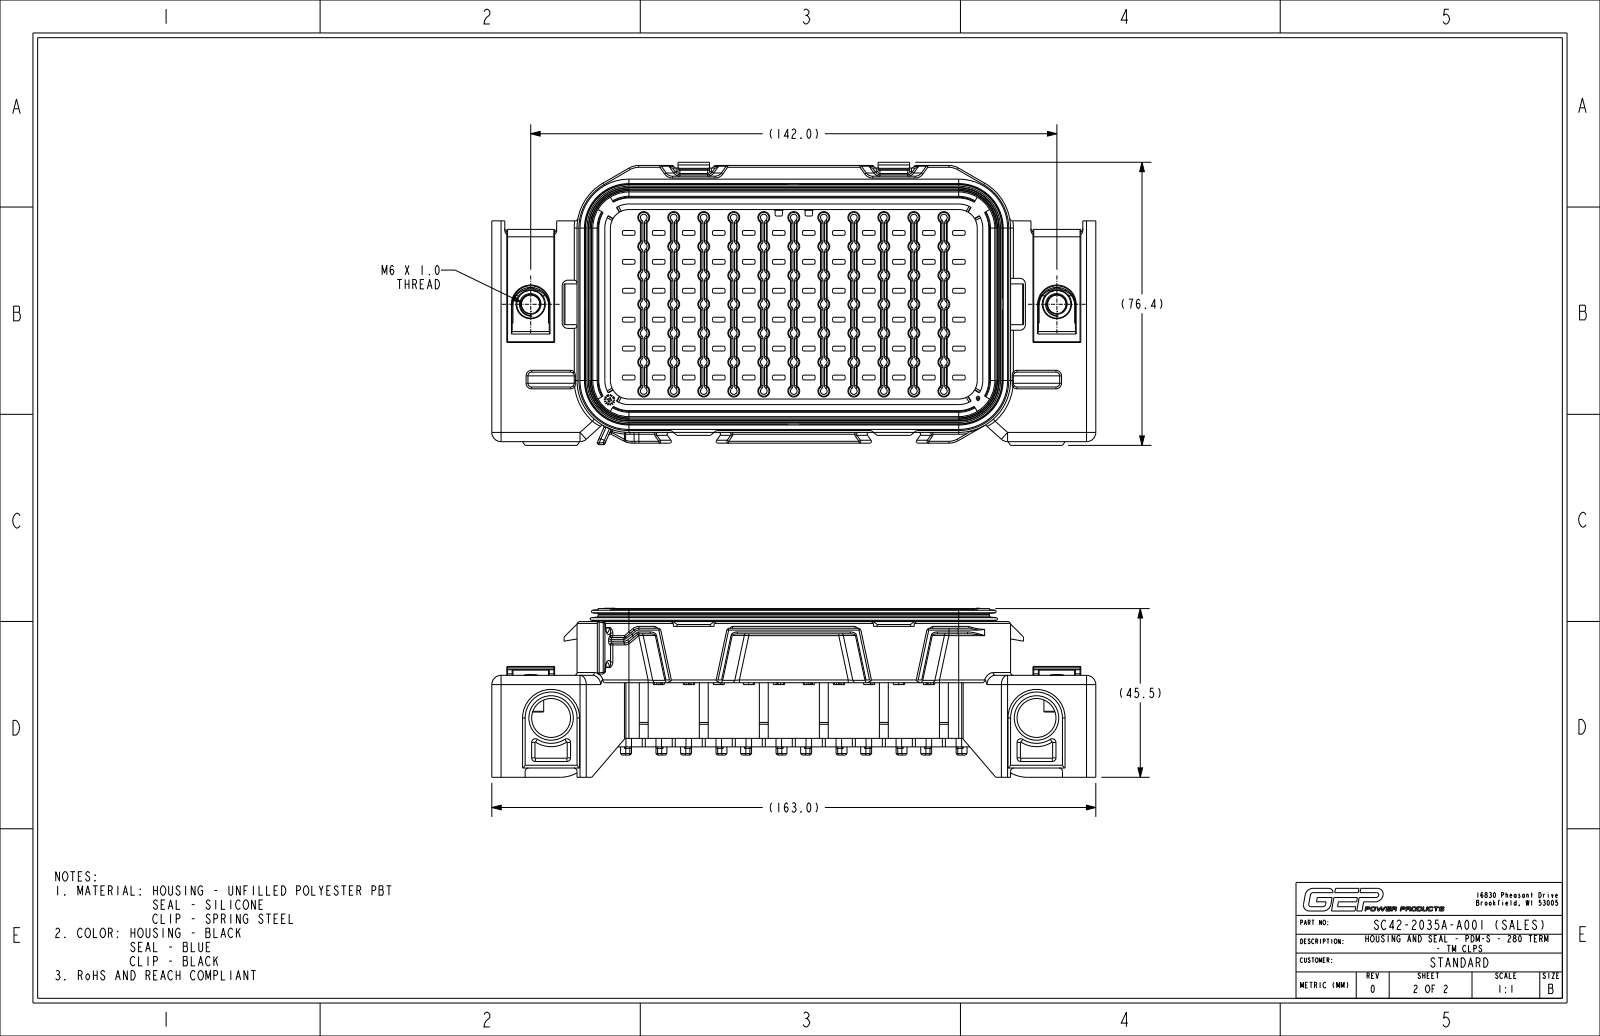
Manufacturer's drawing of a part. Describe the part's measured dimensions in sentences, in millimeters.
The part is named "SC42-2035A-A001_NCF_SW0001". Its 3-D file was written by "CREO PARAMETRIC BY PTC INC, 2024014 (CONFIG_CONTROL_DESIGN)". It is 1 solid with 8064 faces: 2238 planar, 2292 cylindrical and 3534 other. Overall it measures 163 by 76.36 by 45.6 millimeters. Its volume is 173 707 cubic millimeters and its surface area 113 491 square millimeters. Round holes: 72 of diameter 6.7, 4 of diameter 10.5, 2 of diameter 5, 2 of diameter 7.5, 2 of diameter 12.5. Round bosses or shafts: 2 of diameter 7, 1 of diameter 4. Partial cylindrical surfaces (rounded edges, fillets, slot ends): 725 of radius 0.5, 350 of radius 0.4, 77 of radius 1.4, 72 of radius 4.45, 52 of radius 0.2, 52 of radius 0.3, 38 of radius 0.9, 32 of radius 1. The main face-to-face distances are 2, 1.5, 5.5, 7.5, 9, 11.5, 7, 9.5, 2.5, 1.8. The hole center spacings are 17.58, 8.1, 22.49, 16.2, 15.6, 28.88, 35.96, 24.3.
